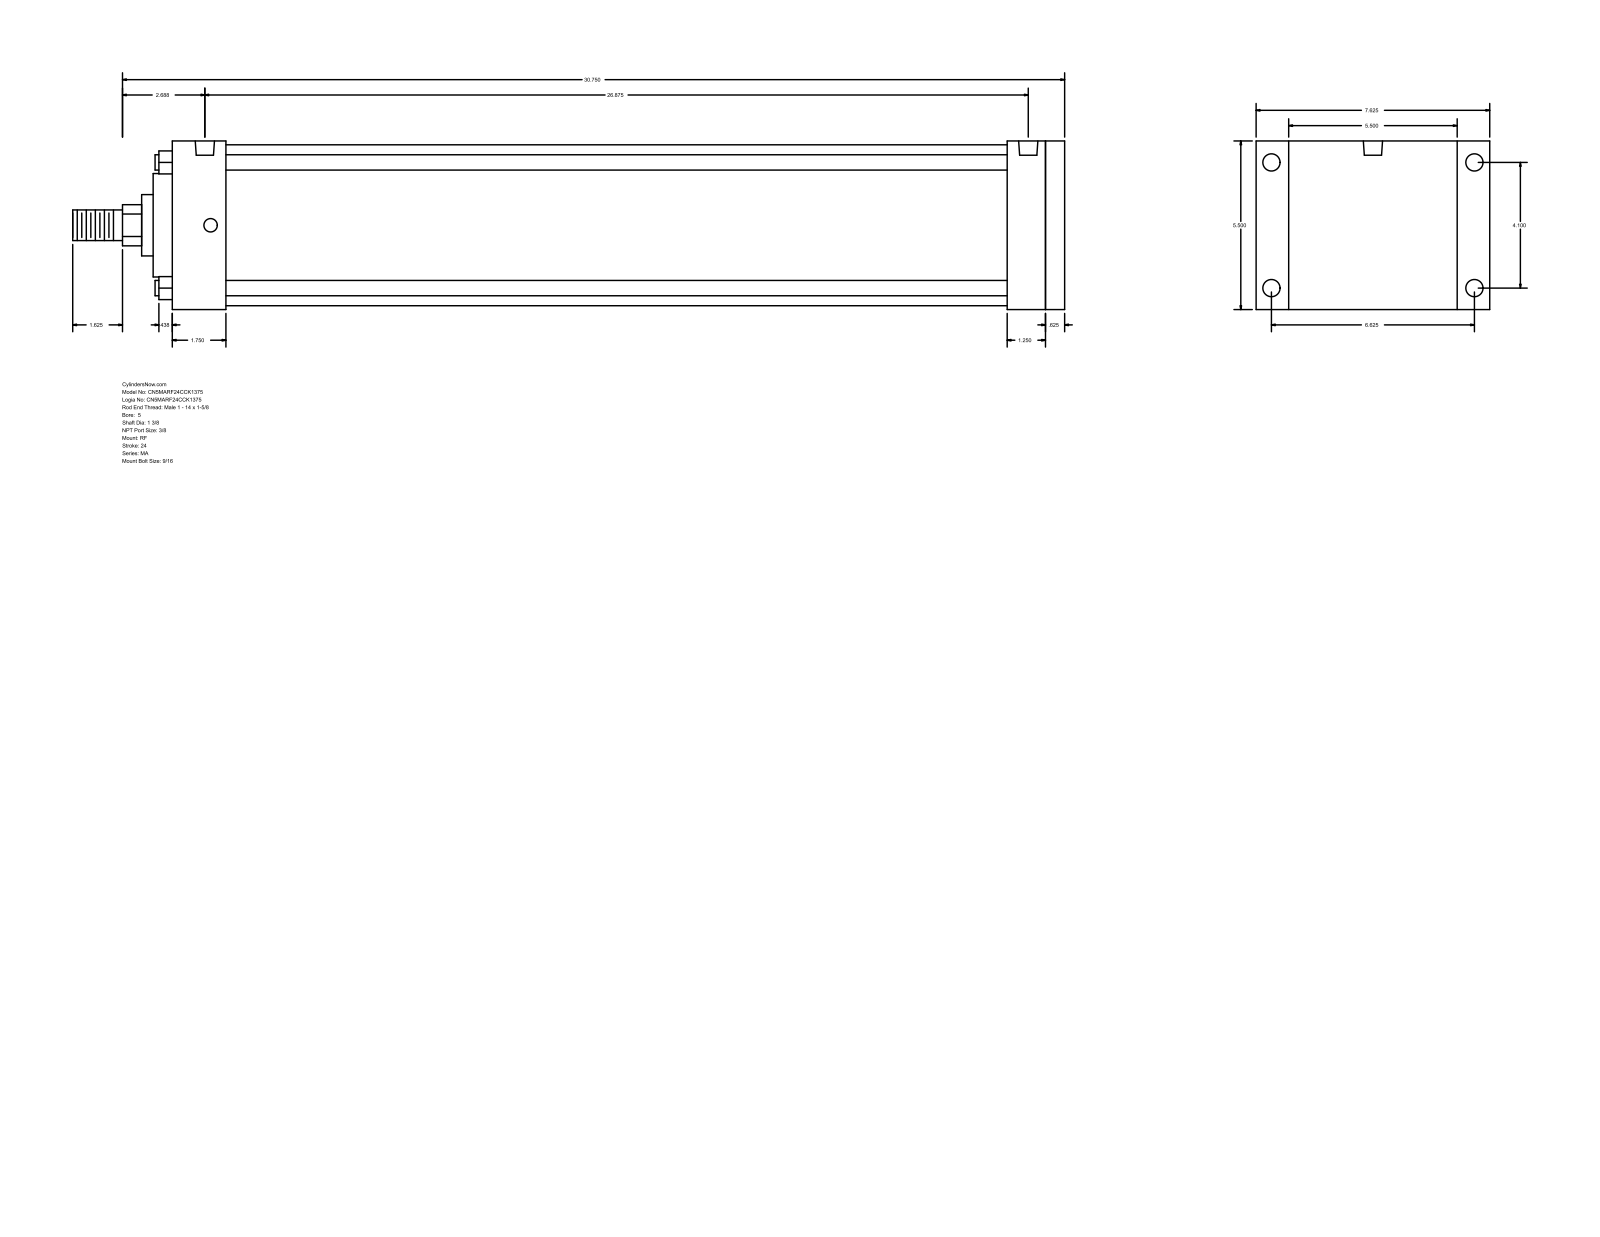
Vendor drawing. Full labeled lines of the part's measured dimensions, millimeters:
Part name (STEP PRODUCT): MA_RF__0500_1.375
STEP written by: GSSL Pune (CONFIG_CONTROL_DESIGN)
Units: millimetres
Bodies: 0 solids, 94 faces (65 planar, 29 cylindrical, 0 other)
Overall size (bounding box): 822.33 × 193.68 × 139.7
Round holes (diameter × count): ⌀11.11 ×4, ⌀14.29 ×4, ⌀15.93 ×2
Round bosses / shafts (diameter × count): ⌀12.7 ×4, ⌀133.35 ×1, ⌀85.72 ×1, ⌀50.8 ×1, ⌀34.92 ×1, ⌀25.4 ×1
Partial cylindrical surfaces — rounded edges, fillets, slot ends (radius × count): R17.06 ×1
Main face-to-face distances: 139.7, 739.78, 15.88, 723.9, 44.45, 679.45, 695.33, 692.15, 647.7, 31.75
Hole centre spacings: 4.77, 104.14, 168.28, 197.9, 673.09, 677.86, 682.63
